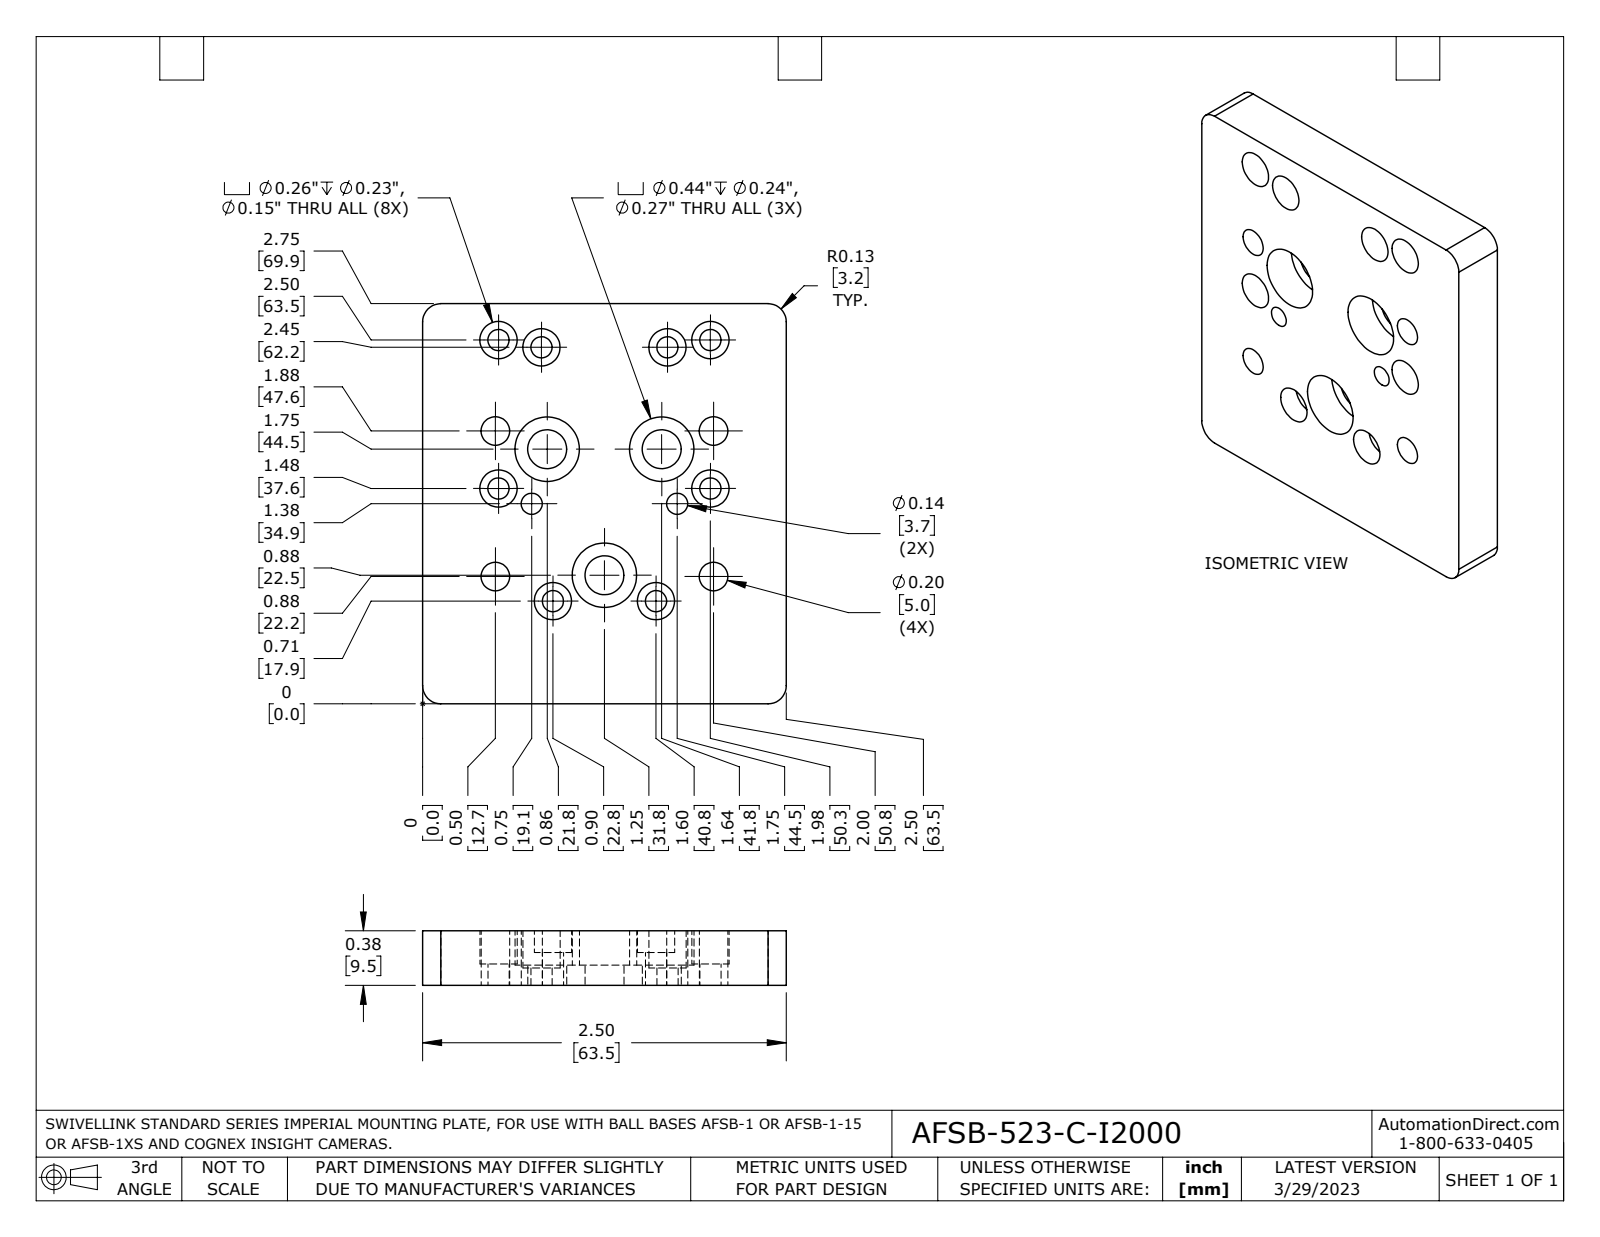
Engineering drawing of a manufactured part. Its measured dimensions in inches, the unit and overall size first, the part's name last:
Units: inches
Overall size (bounding box): 2.75 × 2.5 × 0.375
Round holes (diameter × count): ⌀0.146 ×8, ⌀0.256 ×8, ⌀0.196 ×4, ⌀0.268 ×3, ⌀0.443 ×3, ⌀0.145 ×2
Partial cylindrical surfaces — rounded edges, fillets, slot ends (radius × count): R0.125 ×4
Main face-to-face distances: 0.375, 2.5, 2.75, 0.139, 0.237, 0.147, 0.228, 0.225, 0.087, 0.078
Hole centre spacings: 0.559, 0.701, 1.346, 1, 0.252, 0.3, 0.378, 0.39
Volume: 2.273 in³ · Surface area: 21.24 in²
Bodies: 1 solid, 49 faces (17 planar, 32 cylindrical, 0 other)
Part name (STEP PRODUCT): AFSB-523-C-I2000
STEP written by: SolidWorks 2021 (AUTOMOTIVE_DESIGN)
